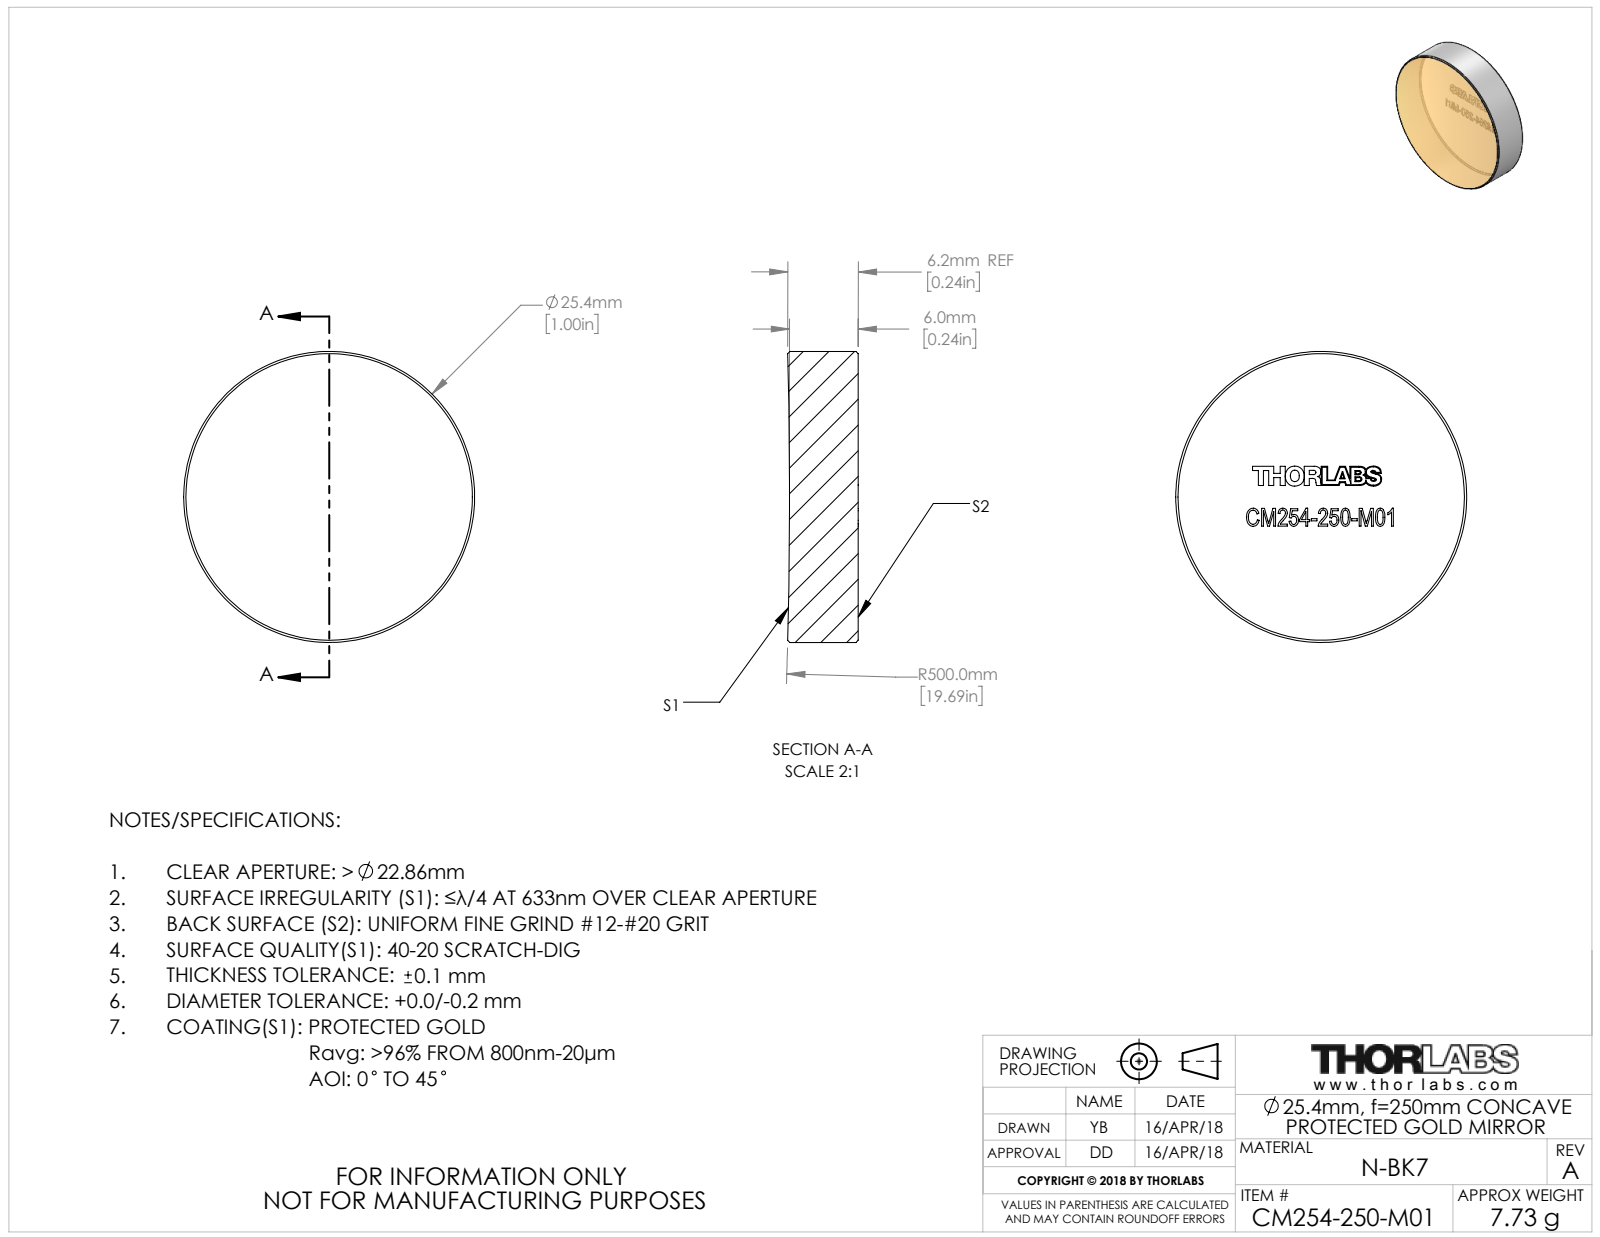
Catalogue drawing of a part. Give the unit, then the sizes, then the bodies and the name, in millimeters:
Units: millimetres
Overall size (bounding box): 25.4 × 25.4 × 6.16
Round bosses / shafts (diameter × count): ⌀25.4 ×1
Volume: 3 078 mm³ · Surface area: 1 486 mm²
Bodies: 1 solid, 40 faces (32 planar, 2 cylindrical, 6 other)
Part name (STEP PRODUCT): TTN153294-E0W
STEP written by: SolidWorks 2018 (CONFIG_CONTROL_DESIGN)
